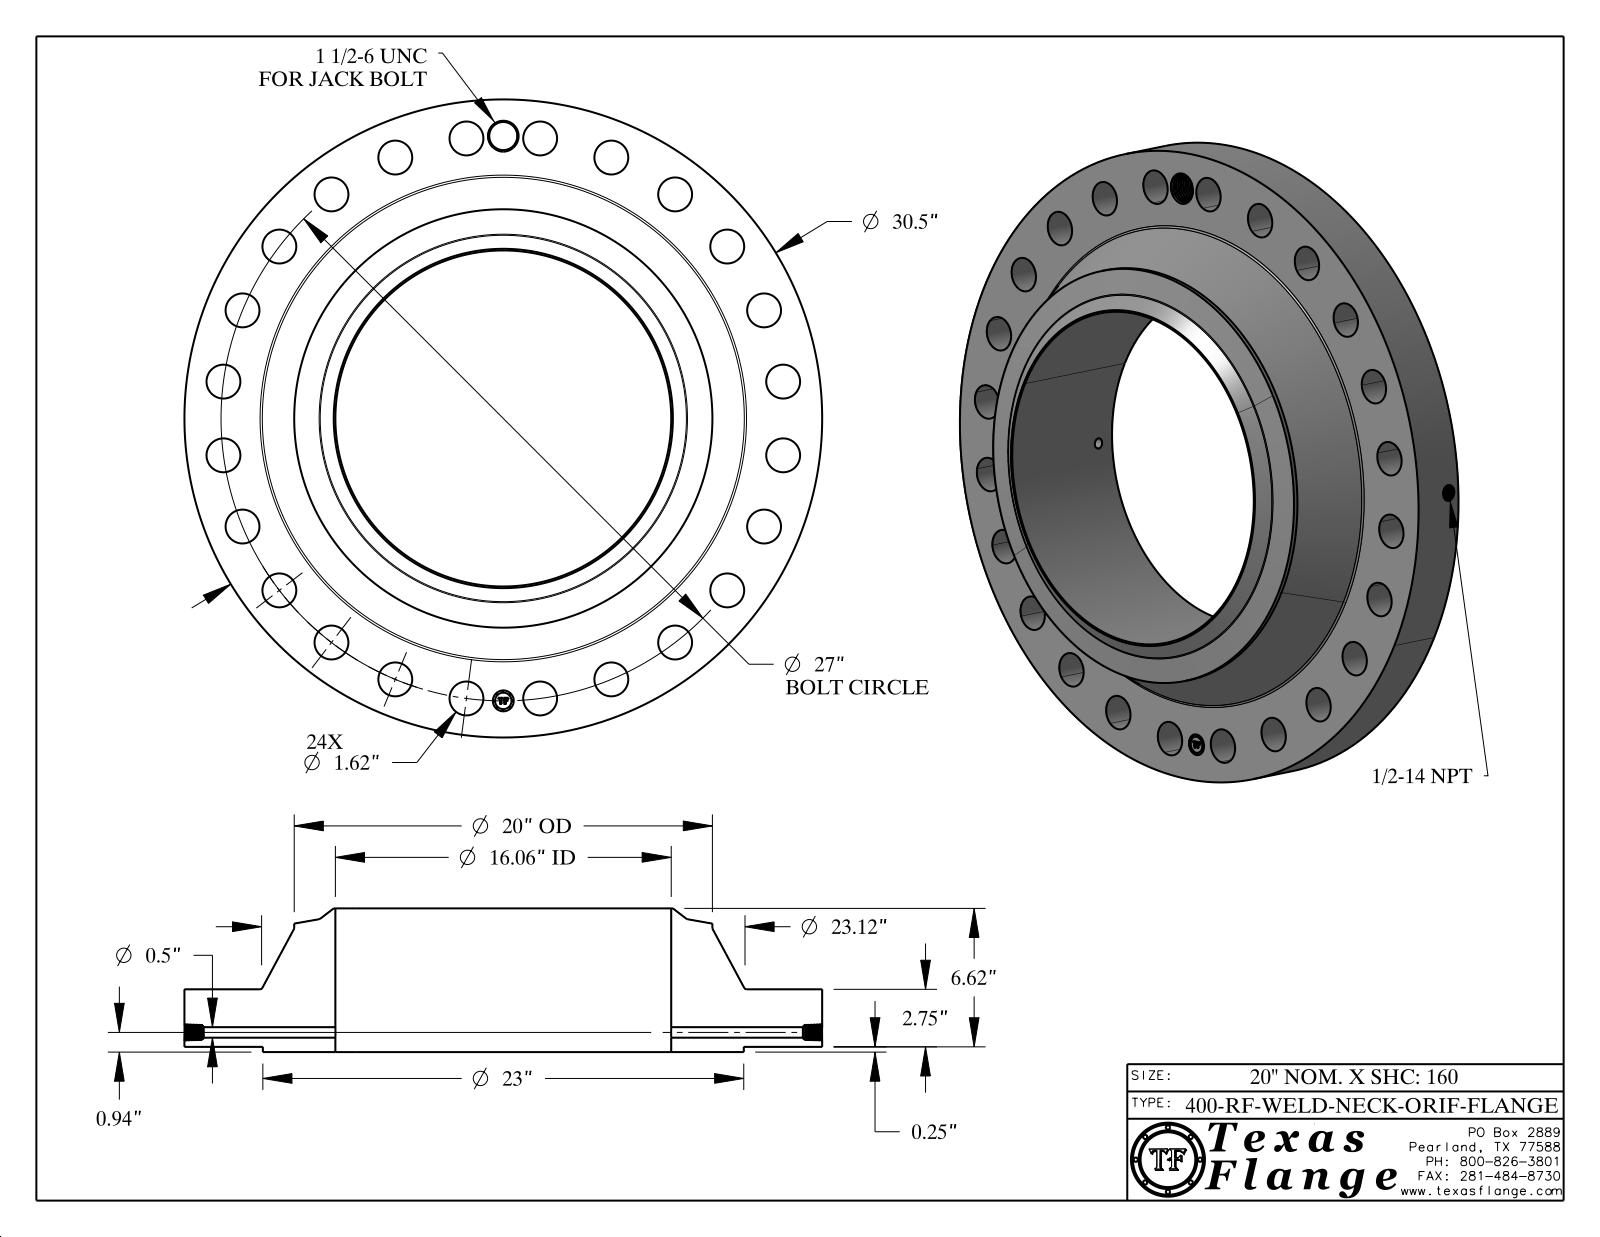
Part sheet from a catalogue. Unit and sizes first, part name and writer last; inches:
Units: inches
Overall size (bounding box): 30.5 × 30.5 × 6.87
Round holes (diameter × count): ⌀1.62 ×24, ⌀0.5 ×1, ⌀0.672 ×1, ⌀1 ×1, ⌀1.344 ×1, ⌀16.062 ×1
Round bosses / shafts (diameter × count): ⌀0.061 ×8, ⌀30.5 ×1, ⌀23 ×1, ⌀20 ×1, ⌀0.788 ×1
Main face-to-face distances: 2.75, 0.25, 3, 6.87, 6.62, 3.87, 2.985, 2.735, 0.015, 3.885
Hole centre spacings: 13.5, 23.383, 24.945, 21.42, 3.524, 6.988, 19.092, 26.08
Volume: 1 889 in³ · Surface area: 2 103 in²
Bodies: 1 solid, 814 faces (369 planar, 129 cylindrical, 316 other)
Part name (STEP PRODUCT): 400-RF-WELD-NECK
STEP written by: CATIA V5 STEP AP214 (AUTOMOTIVE_DESIGN)
